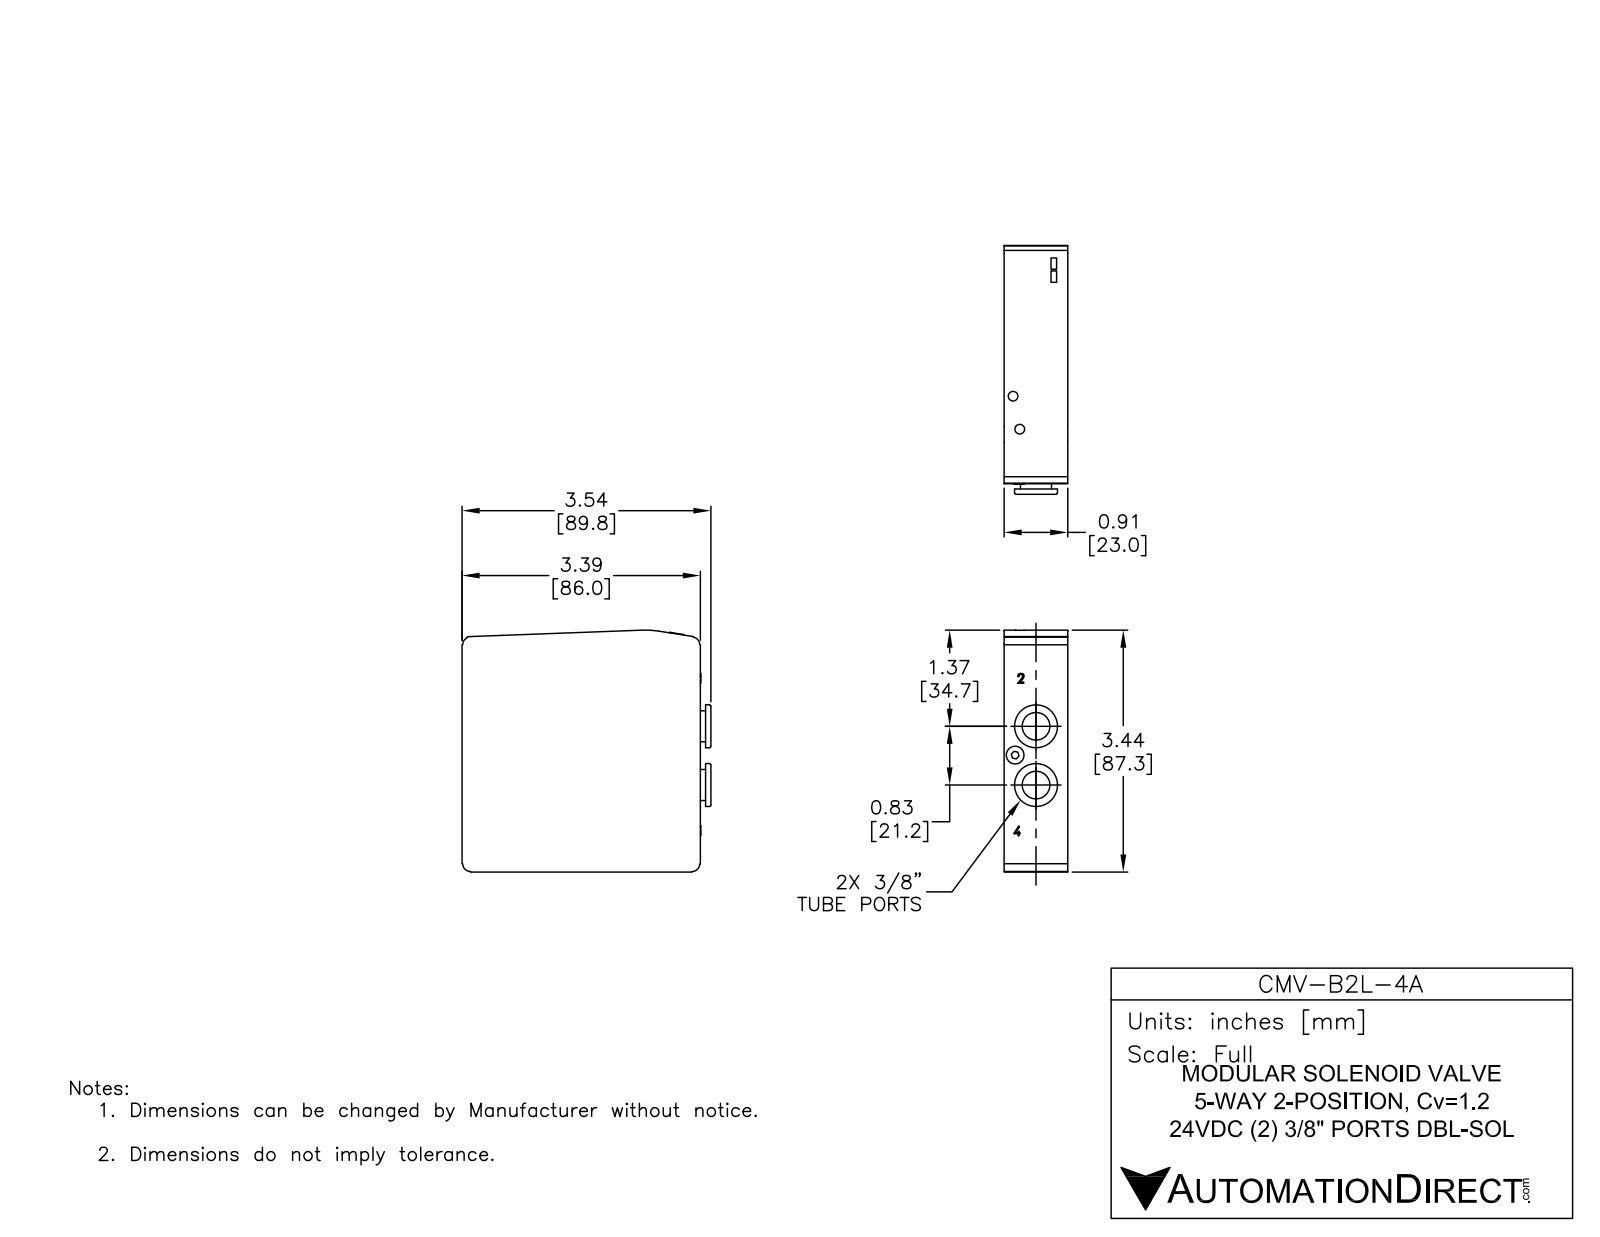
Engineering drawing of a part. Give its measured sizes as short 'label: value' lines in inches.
name: CMV-B2L-4A
written by: SolidWorks 2013 (AUTOMOTIVE_DESIGN)
unit: in
bodies: 75 solids, 1162 faces (896 planar, 162 cylindrical, 104 other)
size: 3.524 × 3.437 × 1.237
volume: 9.4 in³; area: 84.3 in²
holes: 4× ⌀0.173, 4× ⌀0.207, 2× ⌀0.132, 2× ⌀0.256, 2× ⌀0.384, 2× ⌀0.551, 2× ⌀0.709, 1× ⌀0.142, 1× ⌀0.246
bosses: 4× ⌀0.157, 4× ⌀0.059, 2× ⌀0.6, 2× ⌀0.433, 2× ⌀0.246, 2× ⌀0.226, 2× ⌀0.165, 1× ⌀0.138
rounds: 12× R0.093, 4× R0.031, 4× R0.059, 4× R0.11, 2× R0.006, 2× R0.01, 2× R0.039, 2× R0.089
face distances: 0.886, 0.492, 0.394, 3.268, 0.118, 0.039, 2.564, 1.978, 1.289, 2.096
hole spacings: 0.382, 0.472, 0.479, 0.63, 0.873, 1.238, 1.241, 1.555
